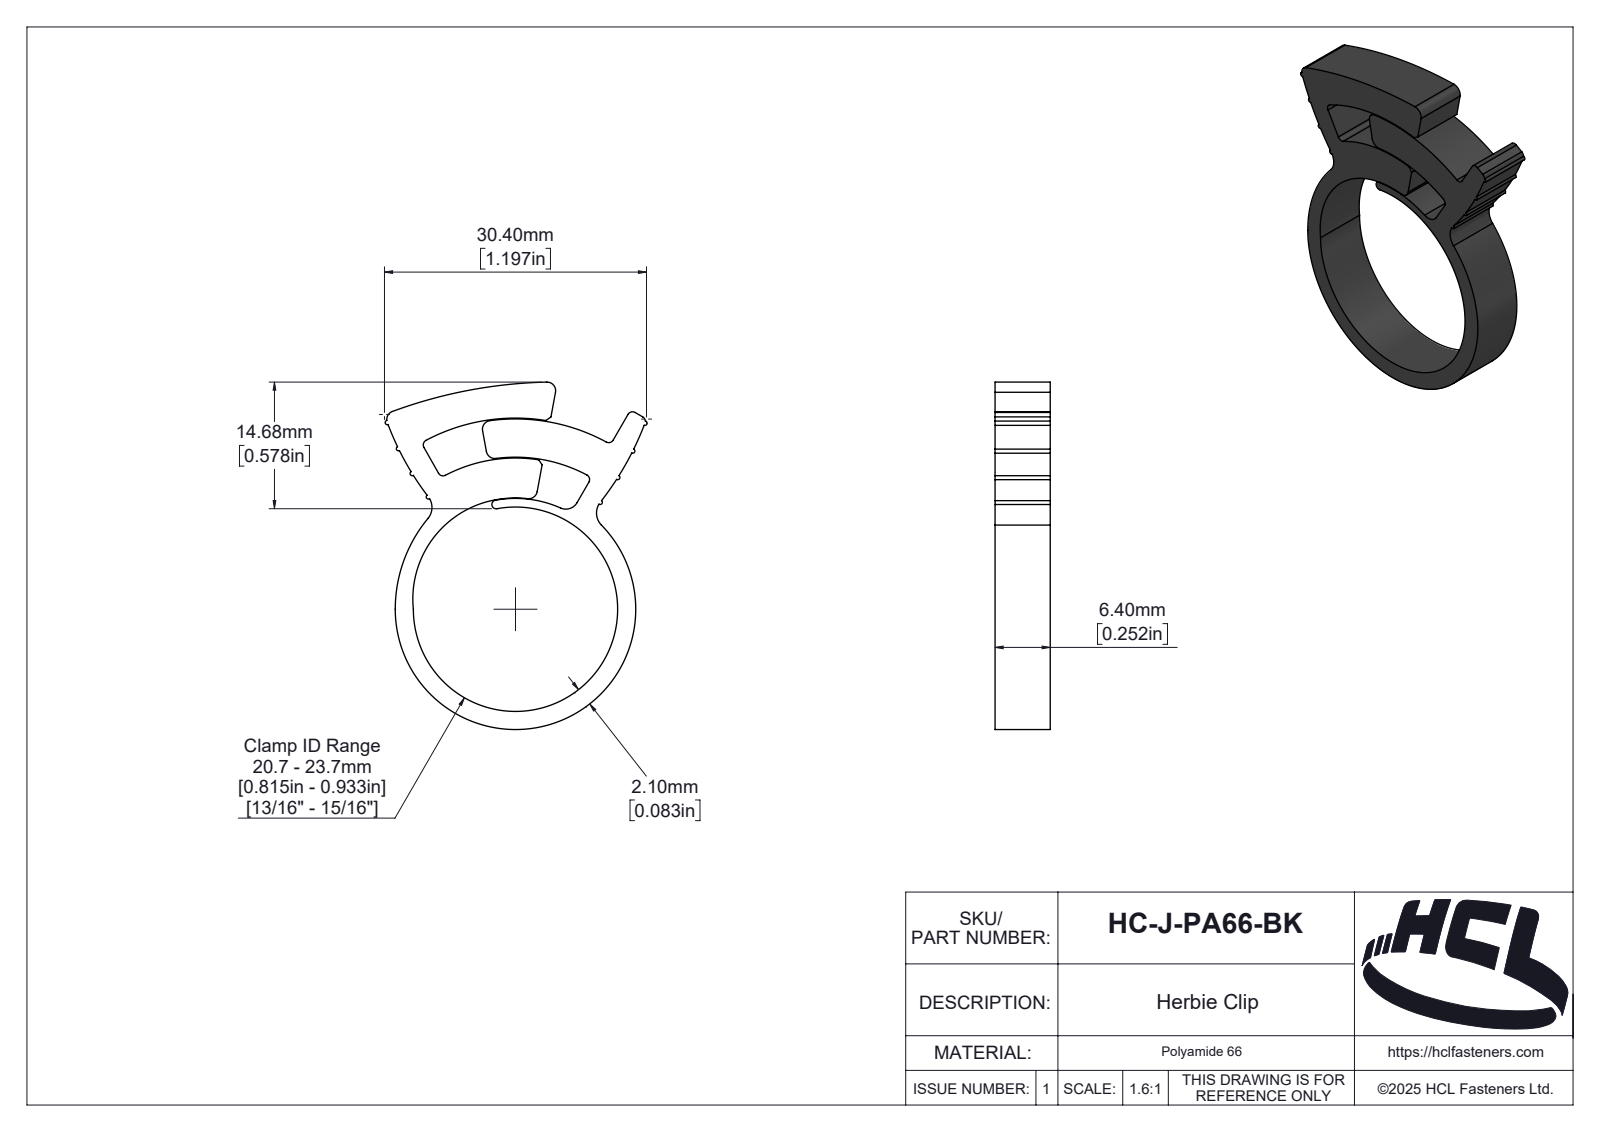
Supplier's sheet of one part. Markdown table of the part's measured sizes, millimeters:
| quantity | value |
| --- | --- |
| part name | HC-J-PA66-BK |
| STEP written by | SolidWorks 2025 (AUTOMOTIVE_DESIGN) |
| units | millimeters |
| bodies | 1 solid, 162 faces (13 planar, 100 cylindrical, 49 other) |
| overall size | 40.29 × 30.39 × 6.4 |
| volume | 2 515 mm³ |
| surface area | 2 632 mm² |
| partial cylindrical surfaces (radius × count) | 0.25 × 8, 0.6 × 6, 1 × 5, 2 × 2, 0.17 × 1, 0.5 × 1, 0.67 × 1, 0.84 × 1 |
| main face-to-face distances | 6.4 |
